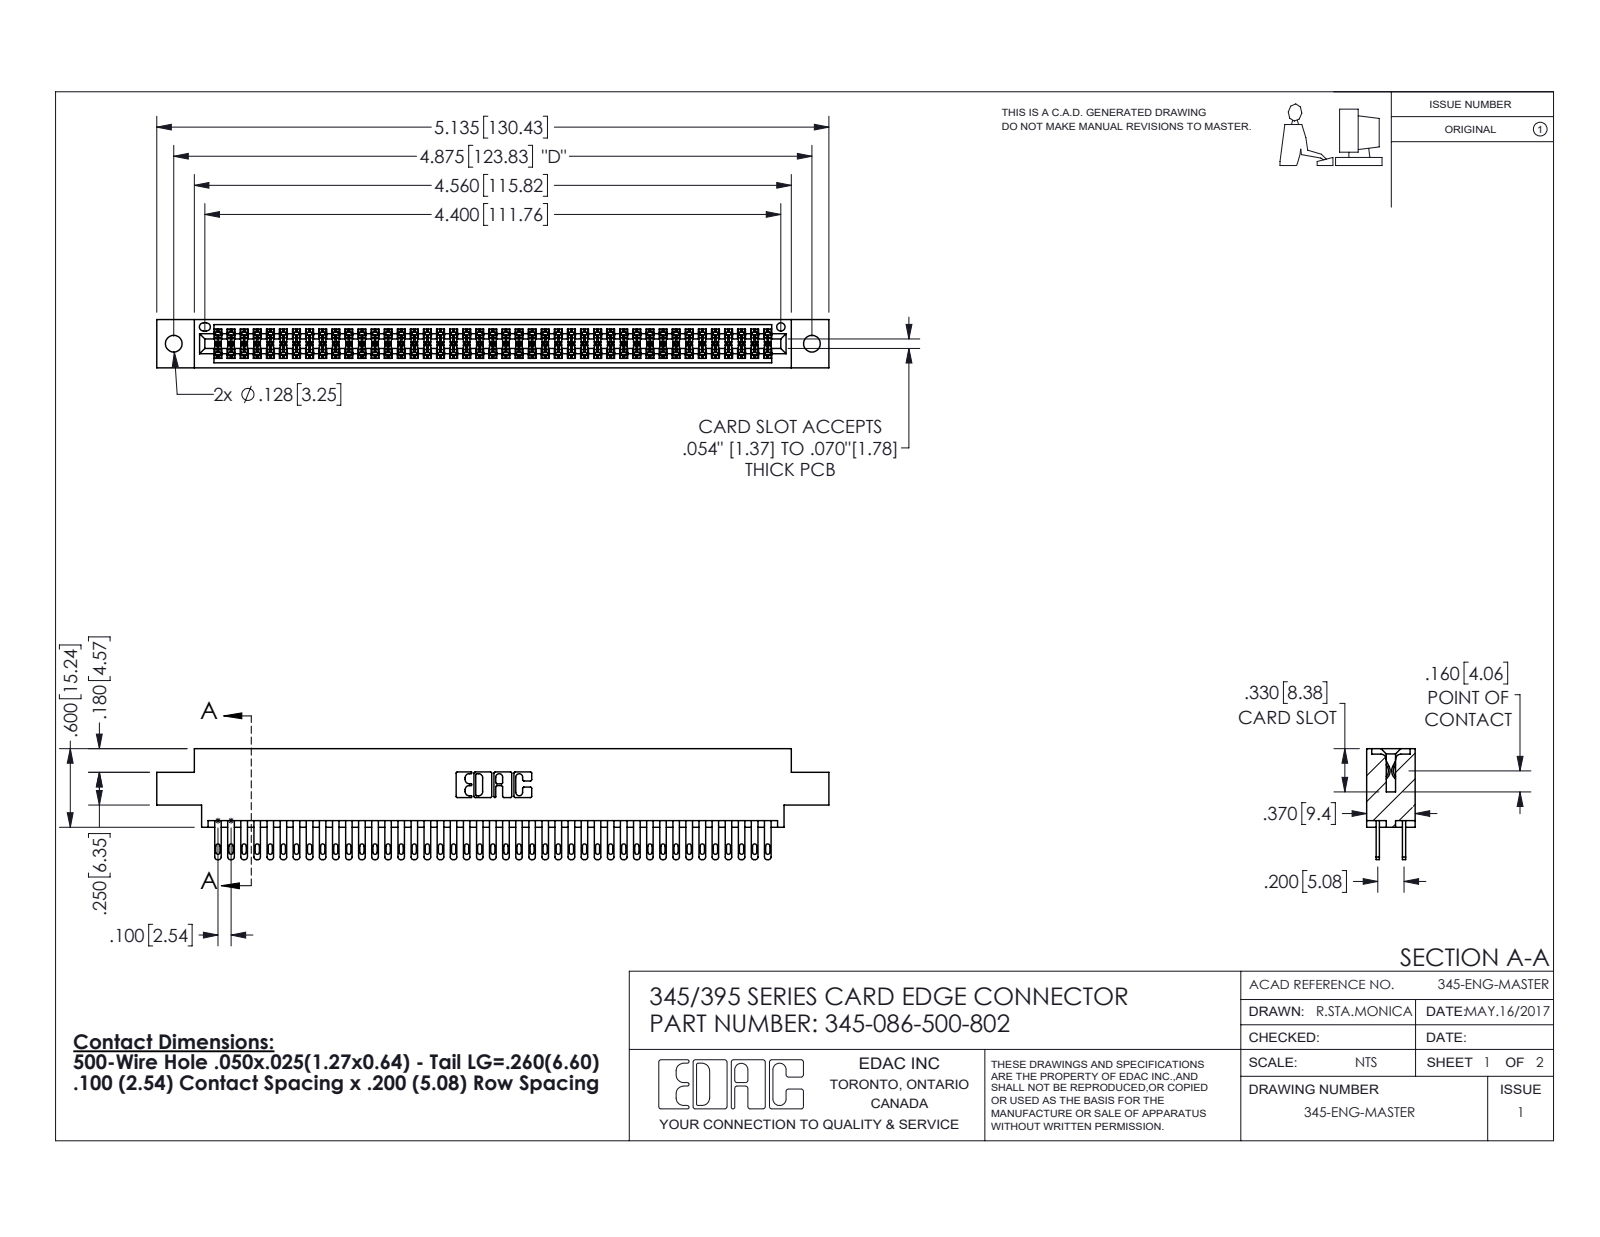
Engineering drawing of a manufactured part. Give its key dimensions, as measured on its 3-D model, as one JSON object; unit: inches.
{"part_name": "345 Part_0.170 Offset - 0.128 Dia; 345-086-500-802; 345-292-001_345-293-100", "step_written_by": "SolidWorks 2016 (CONFIG_CONTROL_DESIGN)", "units": "inches", "bodies": {"solids": 87, "faces": 4086, "planar": 2406, "cylindrical": 1680, "other": 0}, "overall_size": [5.135, 0.847, 0.37], "volume_in3": 0.781, "surface_area_in2": 30.5, "round_holes": [[0.128, 2], [0.064, 1]], "partial_cylinders_radius": [[0.006, 129], [0.016, 86], [0.02, 86], [0.01, 22], [0.007, 6], [0.031, 6], [0.026, 3], [0.014, 2]], "face_to_face_distances": [0.298, 0.072, 0.2, 0.098, 0.272, 0.025, 0.37, 0.225, 0.175, 0.149], "hole_center_spacings": [0.27, 4.639, 4.875]}
